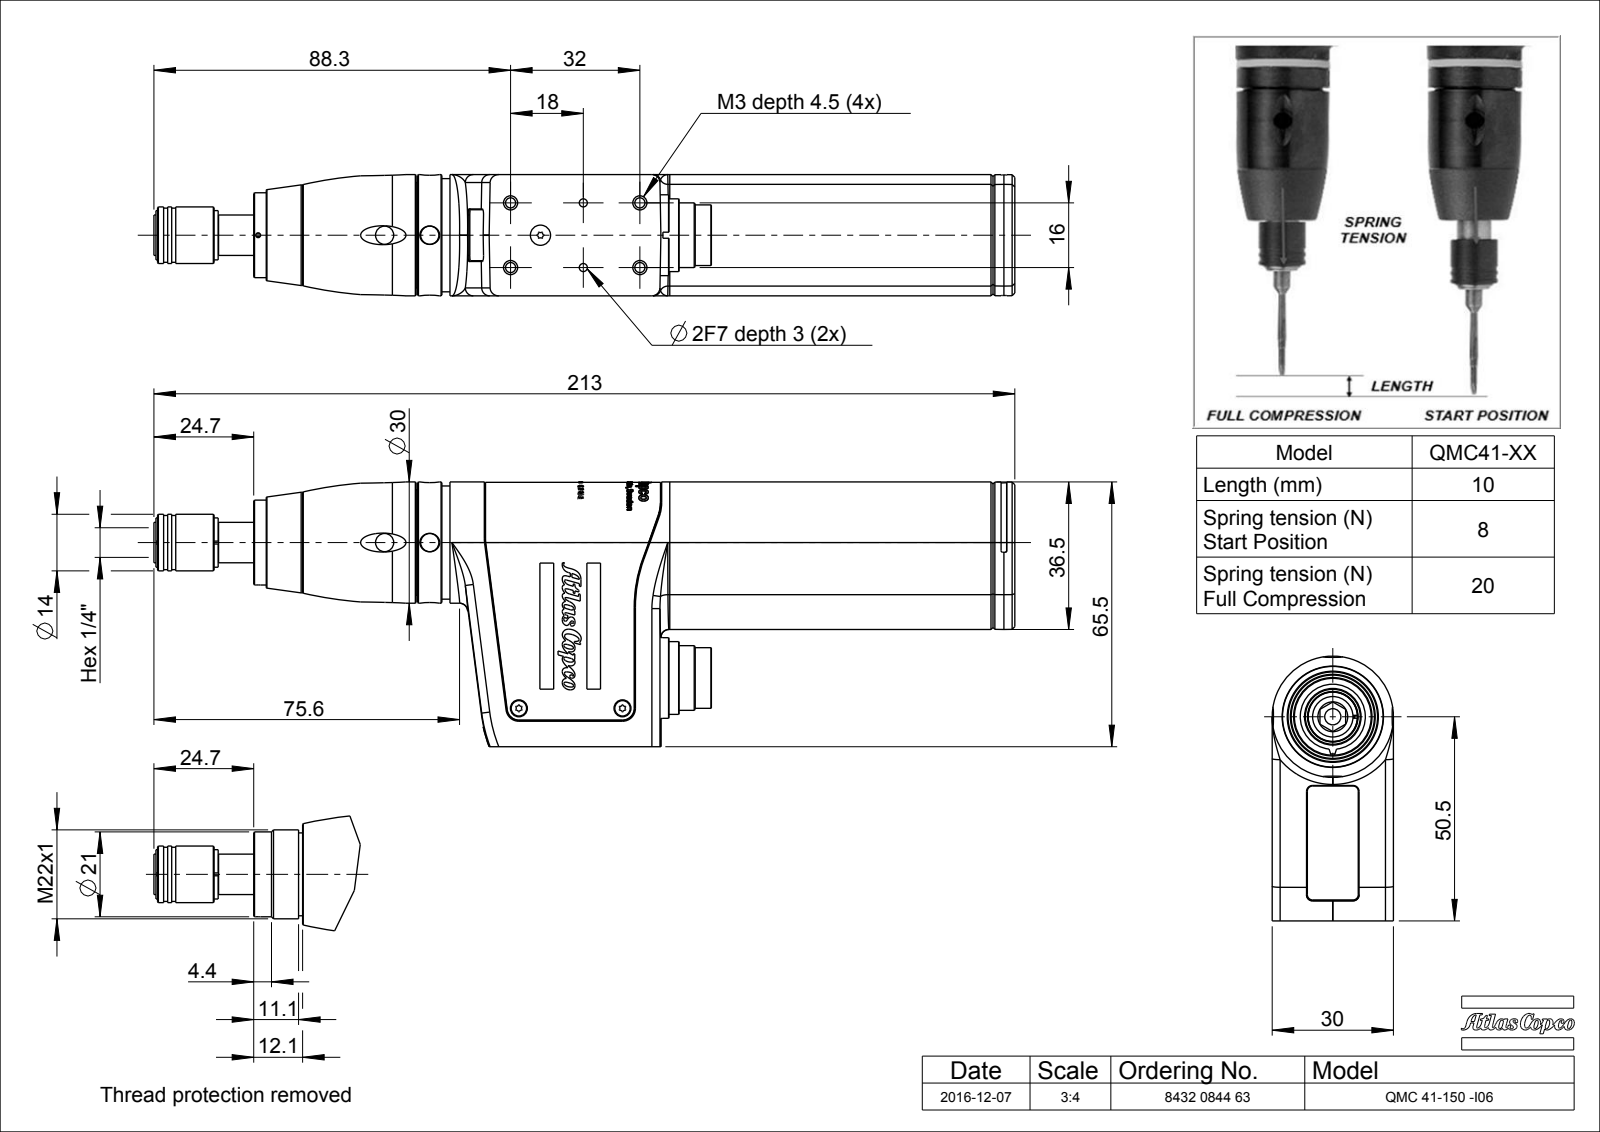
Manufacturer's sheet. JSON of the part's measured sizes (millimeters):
{"part_name": "4216253400; 4216253602; 4216256600; 0993000295_SPEC_3 (+8 more)", "step_written_by": "CREO PARAMETRIC BY PTC INC, 2016260 (CONFIG_CONTROL_DESIGN)", "units": "millimeters", "bodies": {"solids": 23, "faces": 1527, "planar": 401, "cylindrical": 645, "other": 481}, "overall_size": [213.07, 65.5, 30], "volume_mm3": 65011, "surface_area_mm2": 67571, "round_holes": [[2, 5], [1.6, 4], [2.5, 4], [4.5, 4], [2.1, 3], [2.2, 3], [1, 2], [1.2, 2], [2.05, 2], [2.7, 2], [1.1, 1], [4, 1]], "round_bosses_or_shafts": [[1, 12], [0.7, 12], [0.6, 12], [3.8, 5], [2, 3], [20, 2], [30, 1], [28, 1]], "partial_cylinders_radius": [[2, 32], [0.2, 28], [0.1, 18], [0.17, 12], [0.32, 12], [0.53, 12], [1, 9], [0.4, 8]], "face_to_face_distances": [0.7, 29.1, 29.8, 28.4, 0.8, 29.2, 29.9, 2, 30, 1.4], "hole_center_spacings": [16, 17.5, 10.9, 11.17, 13.28, 14, 15.6, 16.26]}
